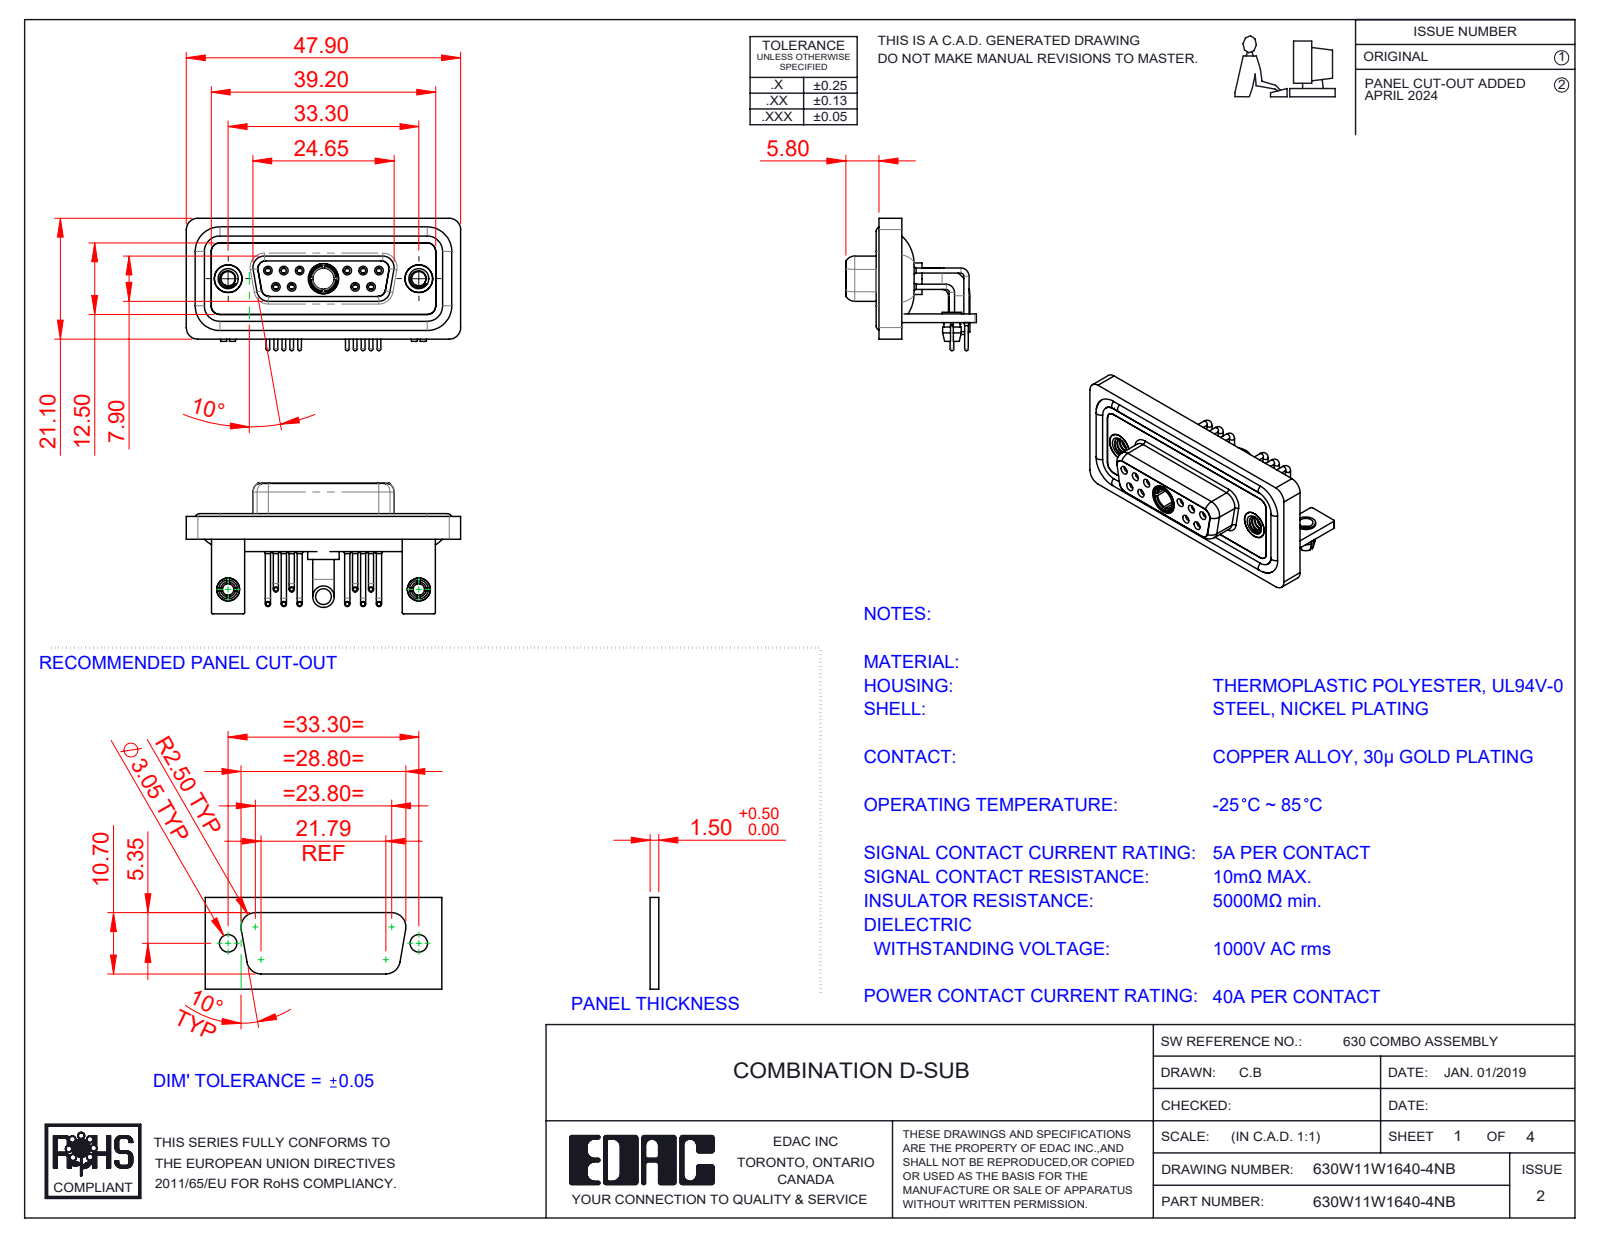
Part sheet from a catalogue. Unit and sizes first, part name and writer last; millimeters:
Units: millimetres
Overall size (bounding box): 47.9 × 23.12 × 22.8
Round holes (diameter × count): ⌀2 ×12, ⌀0.9 ×10, ⌀1.1 ×10, ⌀1.5 ×10, ⌀1.7 ×6, ⌀1.6 ×4, ⌀2.5 ×4, ⌀4.85 ×3, ⌀3.2 ×2, ⌀4 ×2, ⌀4.05 ×2, ⌀5 ×2
Round bosses / shafts (diameter × count): ⌀1.6 ×10, ⌀0.9 ×10, ⌀0.65 ×10, ⌀4.95 ×2, ⌀4.8 ×2, ⌀4 ×2, ⌀3.75 ×2, ⌀3.4 ×2
Partial cylindrical surfaces — rounded edges, fillets, slot ends (radius × count): R2 ×21, R1.5 ×18, R0.25 ×16, R1.35 ×12, R1.6 ×8, R0.5 ×5, R0.6 ×4, R0.65 ×4
Main face-to-face distances: 0.4, 2.9, 1.5, 1.8, 3.7, 1.1, 1.6, 4.1, 0.8, 2.5
Hole centre spacings: 3.16, 2.77, 13.85, 11.08, 16.62, 5.03, 5.04, 5.54
Volume: 6 686 mm³ · Surface area: 11 464 mm²
Bodies: 23 solids, 1128 faces (352 planar, 497 cylindrical, 279 other)
Part name (STEP PRODUCT): 630Combo Shell Front_15 Contacts; 630Combo Housing_11W1; 630Combo Stabilizer Bracket_50 Contacts; 630W11W1640-4NB (+7 more)
STEP written by: SolidWorks 2023 (CONFIG_CONTROL_DESIGN)
